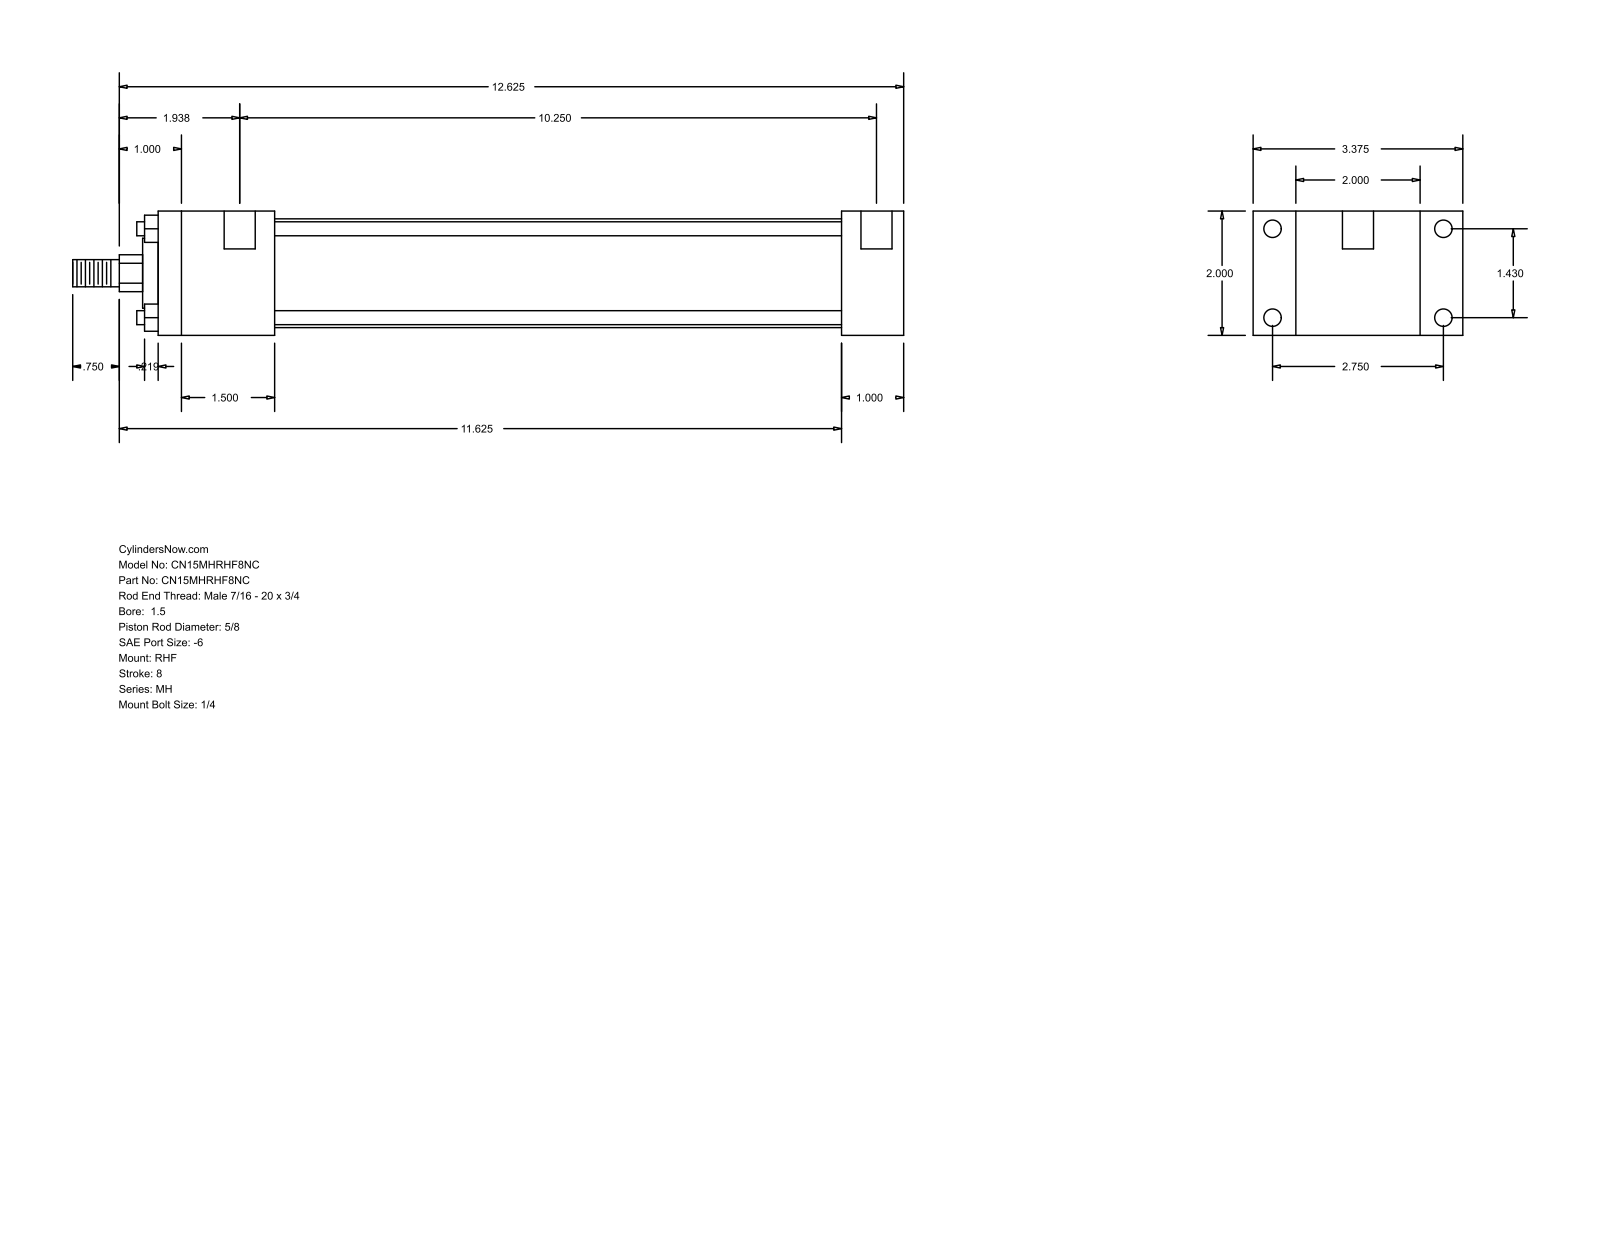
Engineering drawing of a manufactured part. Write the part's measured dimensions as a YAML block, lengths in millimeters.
part_name: "MH_RHF__0150_0.625"
step_written_by: "GSSL Pune (CONFIG_CONTROL_DESIGN)"
units: millimeters
bodies: {solids: 0, faces: 88, planar: 60, cylindrical: 28, other: 0}
overall_size: [339.73, 85.72, 50.8]
round_holes:
  - {diameter: 5.56, count: 4}
  - {diameter: 7.14, count: 4}
  - {diameter: 12.7, count: 2}
round_bosses_or_shafts:
  - {diameter: 5.71, count: 4}
  - {diameter: 44.45, count: 1}
  - {diameter: 28.57, count: 1}
  - {diameter: 15.88, count: 1}
  - {diameter: 11.11, count: 1}
partial_cylinders:
  - {radius: 7.54, count: 1}
face_to_face_distances: [50.8, 17.46, 68.26, 25.41, 279.39, 304.8, 85.72, 47.62, 231.77, 257.18]
hole_center_spacings: [36.32, 69.84, 78.72, 263.52, 3.17, 260.35]
